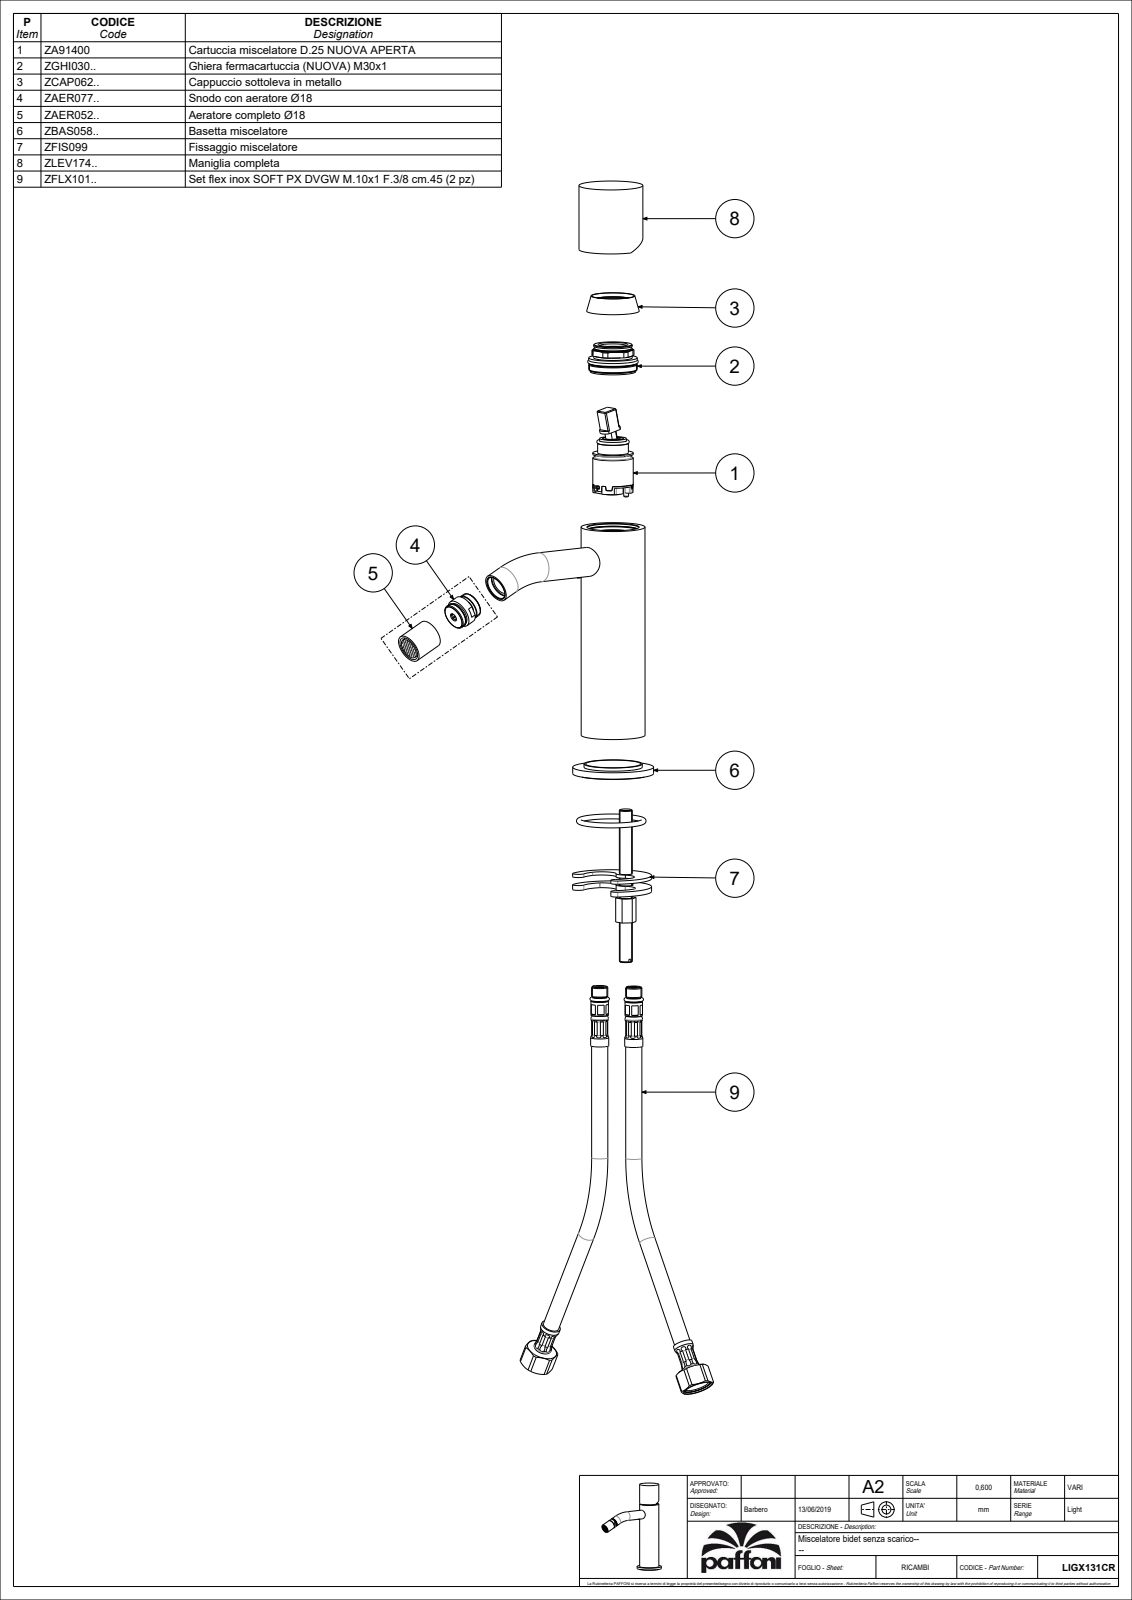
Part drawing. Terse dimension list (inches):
name: LIGX131CR
written by: CREO PARAMETRIC BY PTC INC, 2020044 (CONFIG_CONTROL_DESIGN)
unit: in
bodies: 0 solids, 49 faces (15 planar, 20 cylindrical, 14 other)
size: 6.905 × 5.724 × 1.969
bosses: 4× ⌀0.709, 1× ⌀1.969, 1× ⌀1.555, 1× ⌀0.394, 1× ⌀0.299
rounds: 2× R0.031
face distances: 0.157, 5.276, 5.118, 0.098, 0.217, 0.728, 1.043, 0.315, 0.944, 5.317
